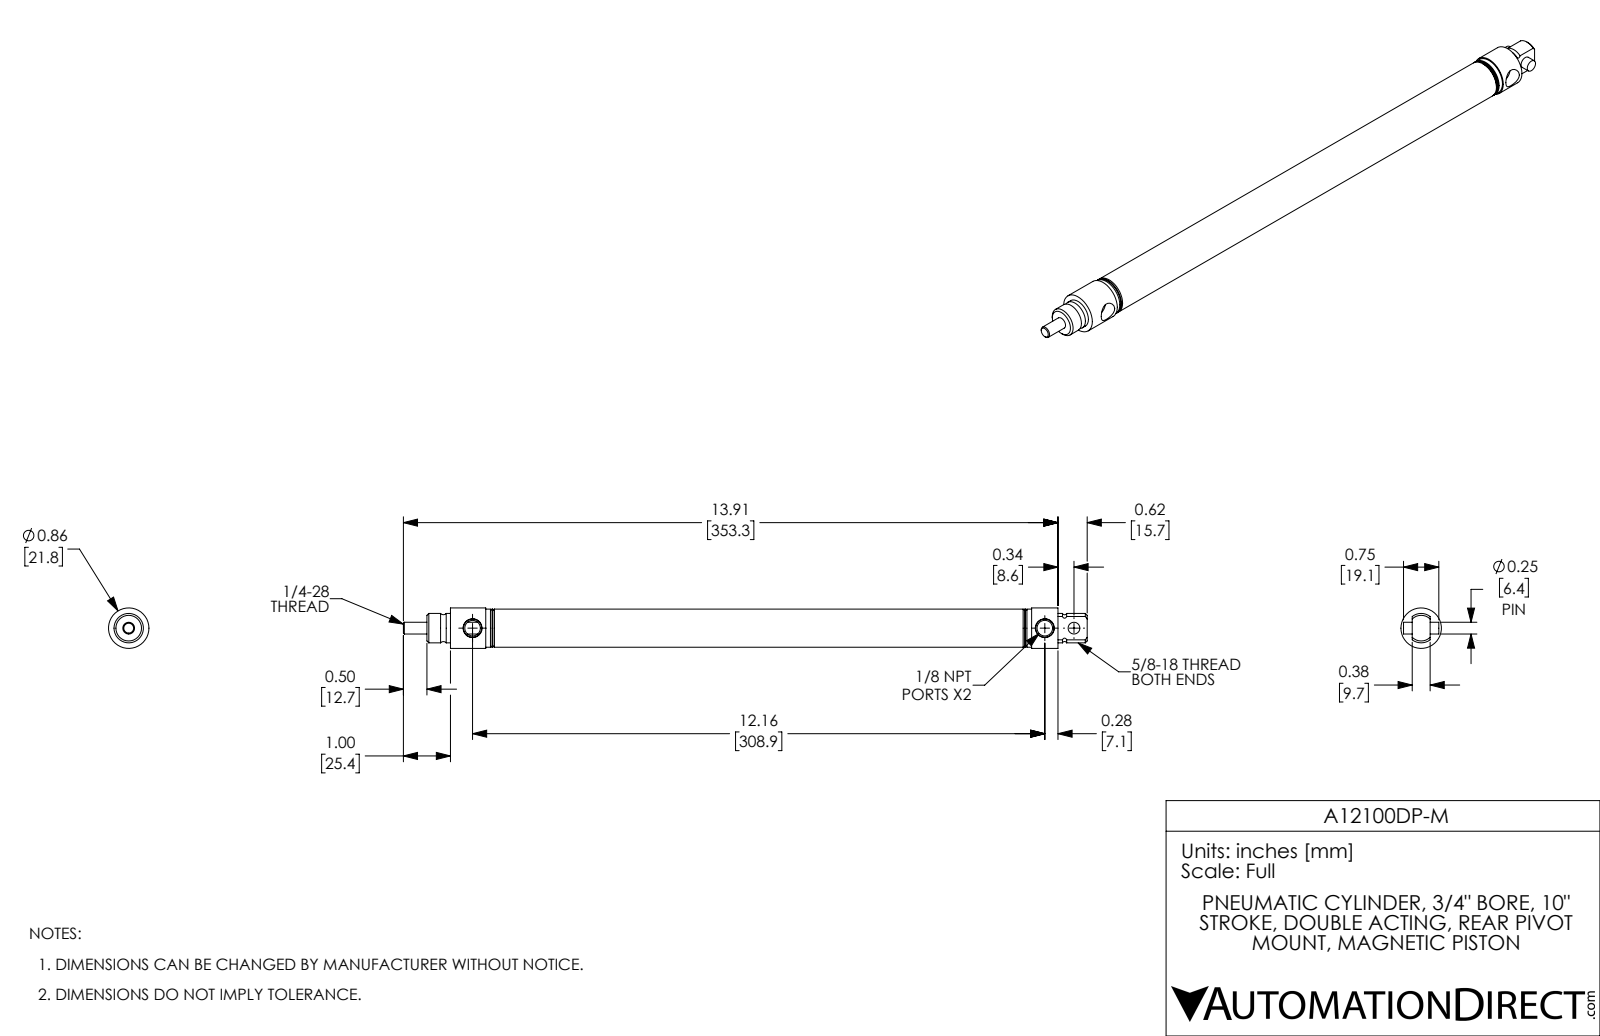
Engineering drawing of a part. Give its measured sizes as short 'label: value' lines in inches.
name: A12100DP-M-MainBody; A12100DP-M-Rod; A12100DP-M-PIN; A12100DP-M
written by: SolidWorks 2017 (AUTOMOTIVE_DESIGN)
unit: in
bodies: 3 solids, 91 faces (21 planar, 38 cylindrical, 32 other)
size: 14.53 × 0.86 × 0.86
volume: 3.042 in³; area: 76.96 in²
holes: 2× ⌀0.25, 2× ⌀0.332, 1× ⌀0.75
bosses: 1× ⌀0.86, 1× ⌀0.81, 1× ⌀0.625
face distances: 0.5, 11.705, 10.5, 10, 1.205, 1.705, 11.705, 12.91, 11.205, 1.205
hole spacings: 0.62, 12.16, 12.78
